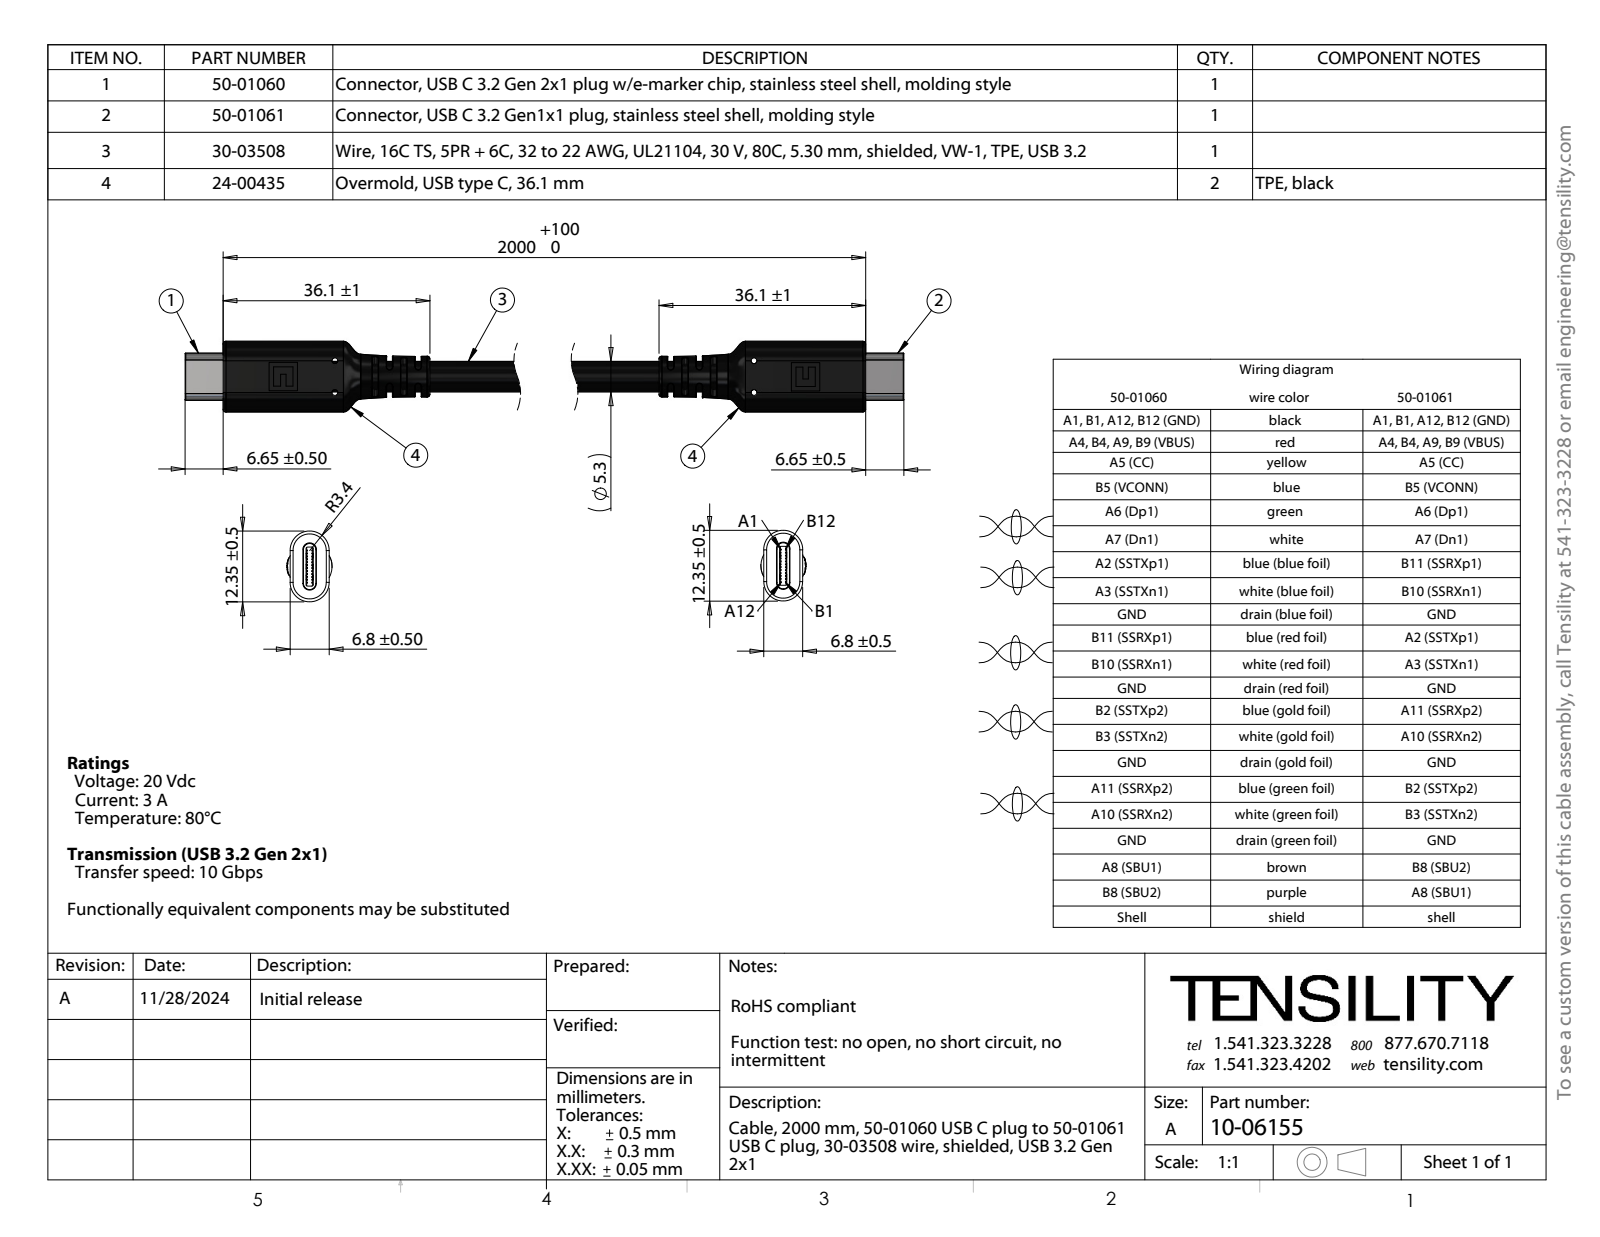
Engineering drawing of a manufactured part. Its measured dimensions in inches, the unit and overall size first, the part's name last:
Units: inches
Overall size (bounding box): 7.775 × 0.486 × 0.311
Round holes (diameter × count): ⌀0.039 ×4, ⌀0.164 ×1, ⌀0.164 ×1, ⌀0.165 ×1, ⌀0.165 ×1, ⌀0.173 ×1
Round bosses / shafts (diameter × count): ⌀0.029 ×8, ⌀0.019 ×4, ⌀0.01 ×4, ⌀0.022 ×2, ⌀0.308 ×1, ⌀0.209 ×1, ⌀0.039 ×1, ⌀0.035 ×1
Partial cylindrical surfaces — rounded edges, fillets, slot ends (radius × count): R0.02 ×20, R0.01 ×8, R0.004 ×4, R0.006 ×4, R0.012 ×2, R0.012 ×2, R0.019 ×2, R0.019 ×2
Main face-to-face distances: 0.041, 0.041, 0.037, 0.04, 0.043, 0.268, 0.024, 0.026, 0.087, 0.067
Hole centre spacings: 0.097, 0.083, 0.081, 0.098, 0.025, 0.065, 0.084, 0.022
Volume: 0.413 in³ · Surface area: 76.59 in²
Bodies: 168 solids, 1726 faces (728 planar, 766 cylindrical, 232 other)
Part name (STEP PRODUCT): 10-06155; 24-00435; 50-01060; 50-01061_Hidden emarker (+1 more)
STEP written by: SolidWorks 2021 (CONFIG_CONTROL_DESIGN)
